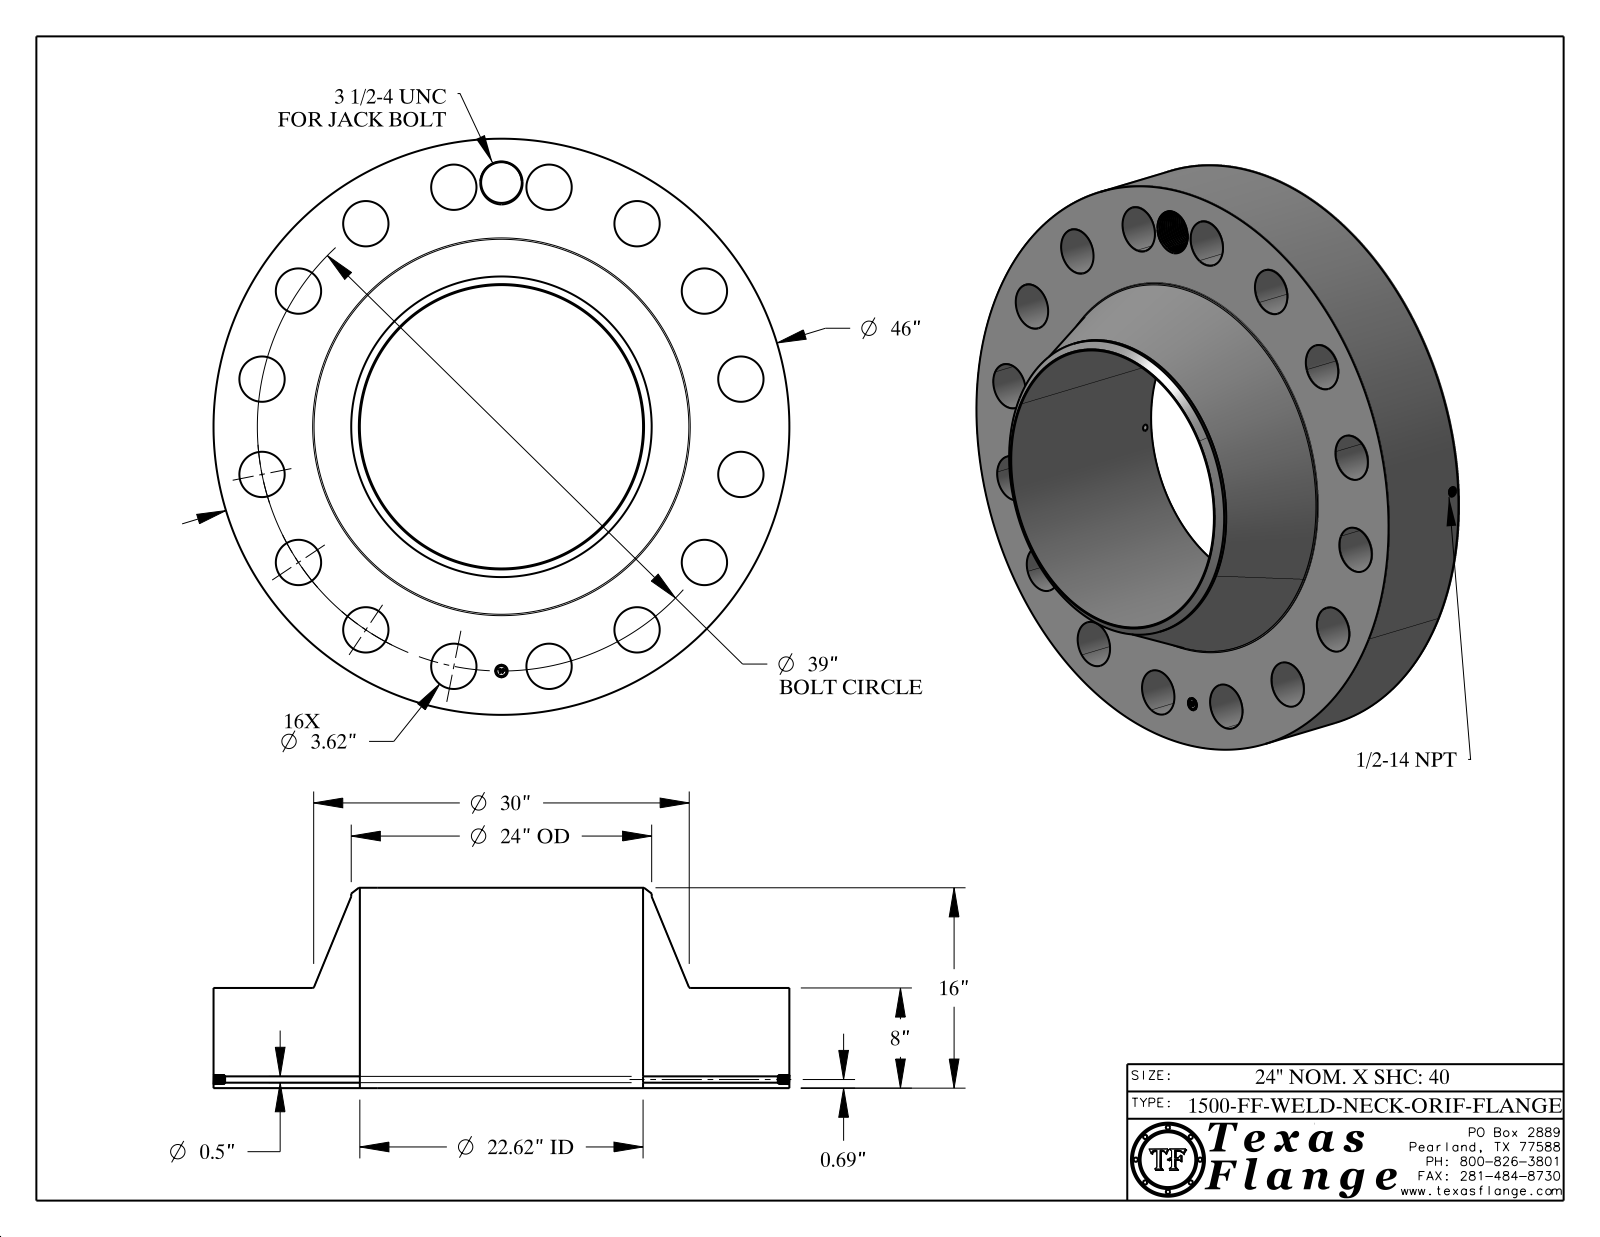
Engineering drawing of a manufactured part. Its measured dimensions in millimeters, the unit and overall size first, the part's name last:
Units: millimetres
Overall size (bounding box): 1168.4 × 1168.4 × 406.4
Round holes (diameter × count): ⌀91.9 ×16, ⌀12.7 ×1, ⌀17.1 ×1, ⌀25.4 ×1, ⌀82.6 ×1, ⌀574.6 ×1
Round bosses / shafts (diameter × count): ⌀1.5 ×8, ⌀1168.4 ×1, ⌀609.6 ×1, ⌀20 ×1
Main face-to-face distances: 203.2, 406.4, 202.8, 0.4, 203.6, 7.6, 7.4, 1.4, 6.3, 4.9
Hole centre spacings: 495.3, 700.5, 915.2, 823.6, 193.2, 379.1, 379.1, 550.3
Volume: 163 400 000 mm³ · Surface area: 4 209 000 mm²
Bodies: 1 solid, 884 faces (368 planar, 142 cylindrical, 374 other)
Part name (STEP PRODUCT): 1500-FF-WELD-NECK
STEP written by: CATIA V5 STEP AP214 (AUTOMOTIVE_DESIGN)
